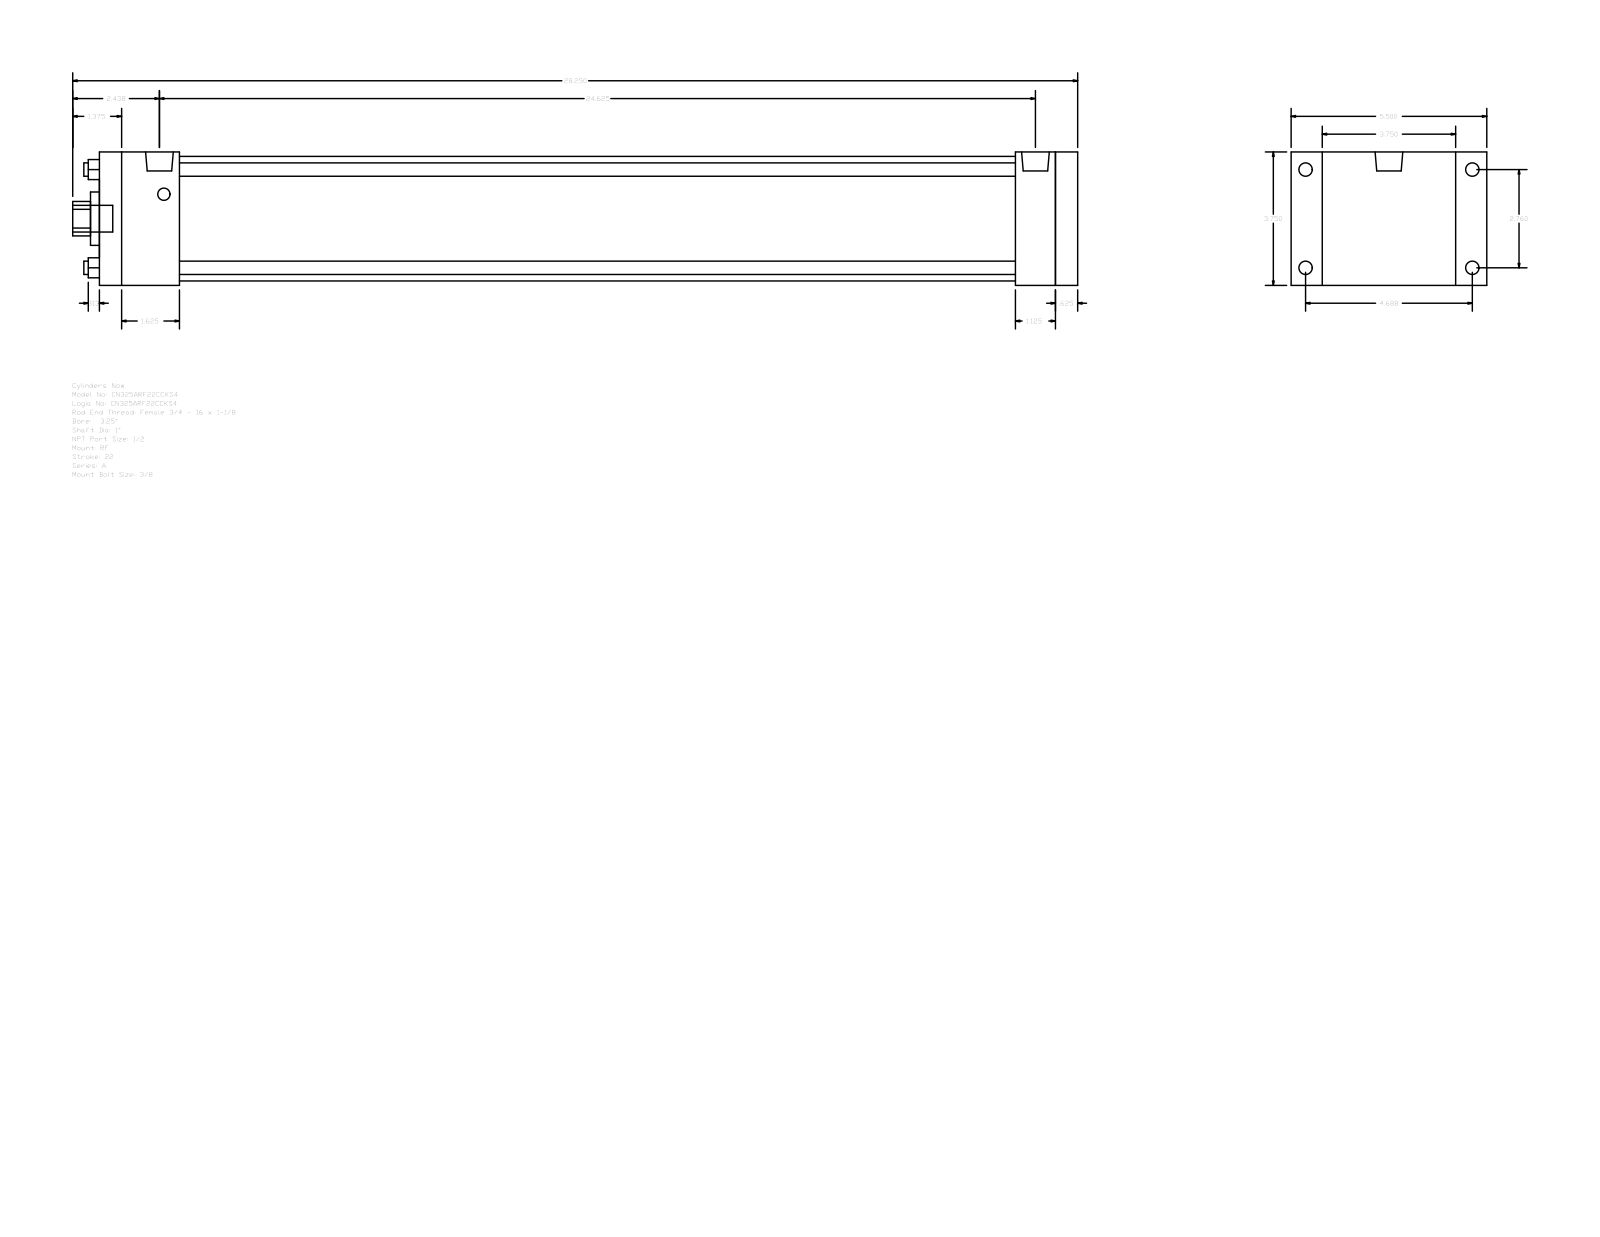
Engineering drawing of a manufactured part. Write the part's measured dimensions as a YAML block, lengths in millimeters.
part_name: "A_RF__0325_1"
step_written_by: "GSSL Pune (CONFIG_CONTROL_DESIGN)"
units: millimeters
bodies: {solids: 0, faces: 92, planar: 64, cylindrical: 28, other: 0}
overall_size: [717.55, 139.7, 95.25]
round_holes:
  - {diameter: 9.53, count: 4}
  - {diameter: 25.4, count: 1}
  - {diameter: 38.1, count: 1}
  - {diameter: 88.9, count: 1}
round_bosses_or_shafts:
  - {diameter: 9.53, count: 4}
  - {diameter: 8.73, count: 4}
  - {diameter: 19.77, count: 2}
  - {diameter: 19.05, count: 1}
partial_cylinders:
  - {radius: 12.29, count: 1}
face_to_face_distances: [95.24, 698.5, 682.62, 15.88, 22.23, 117.47, 28.57, 654.05, 44.45, 57.15]
hole_center_spacings: [49.57, 70.1, 99.14]
